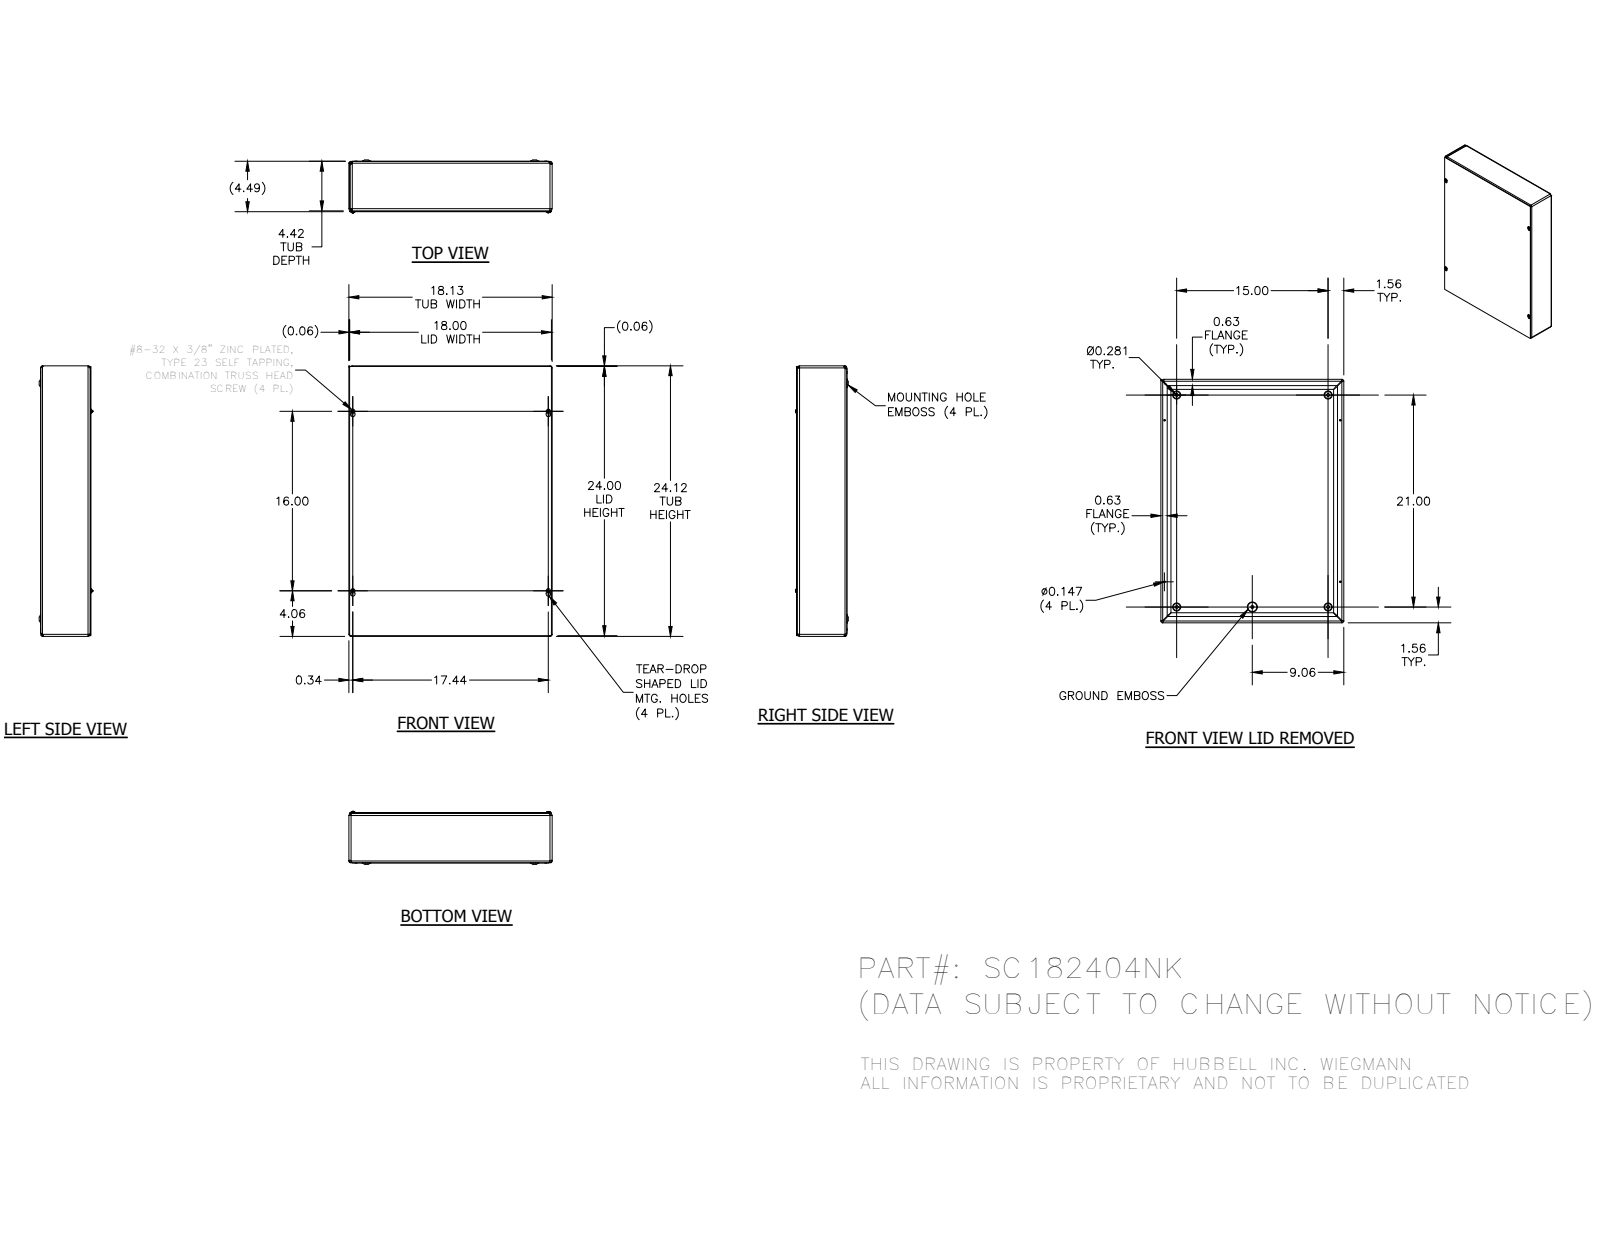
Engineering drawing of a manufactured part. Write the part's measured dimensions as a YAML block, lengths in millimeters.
part_name: "SC1824BKP; SC182404NKWRA; SC1824LID; 34056 (+1 more)"
step_written_by: "Autodesk Inventor 2014 (AUTOMOTIVE_DESIGN)"
units: millimeters
bodies: {solids: 7, faces: 358, planar: 133, cylindrical: 75, other: 150}
overall_size: [612.77, 460.38, 119.79]
volume: 1521000
surface_area: 1738000
round_holes:
  - {diameter: 3.73, count: 4}
  - {diameter: 7.62, count: 4}
  - {diameter: 4.19, count: 1}
round_bosses_or_shafts:
  - {diameter: 4.57, count: 8}
  - {diameter: 9.75, count: 4}
  - {diameter: 4.17, count: 4}
  - {diameter: 5.8, count: 1}
partial_cylinders:
  - {radius: 3.17, count: 12}
  - {radius: 4.75, count: 8}
  - {radius: 1.4, count: 4}
  - {radius: 1.57, count: 4}
  - {radius: 2.38, count: 4}
  - {radius: 2.97, count: 4}
  - {radius: 3.15, count: 4}
  - {radius: 3.96, count: 4}
face_to_face_distances: [1.88, 112.2, 110.32, 114.08, 1.57, 458.8, 611.2, 457.23, 460.37, 612.77]
hole_center_spacings: [470.92, 624.91, 70.64, 70.65, 190.5, 381, 406.4, 416.82]
